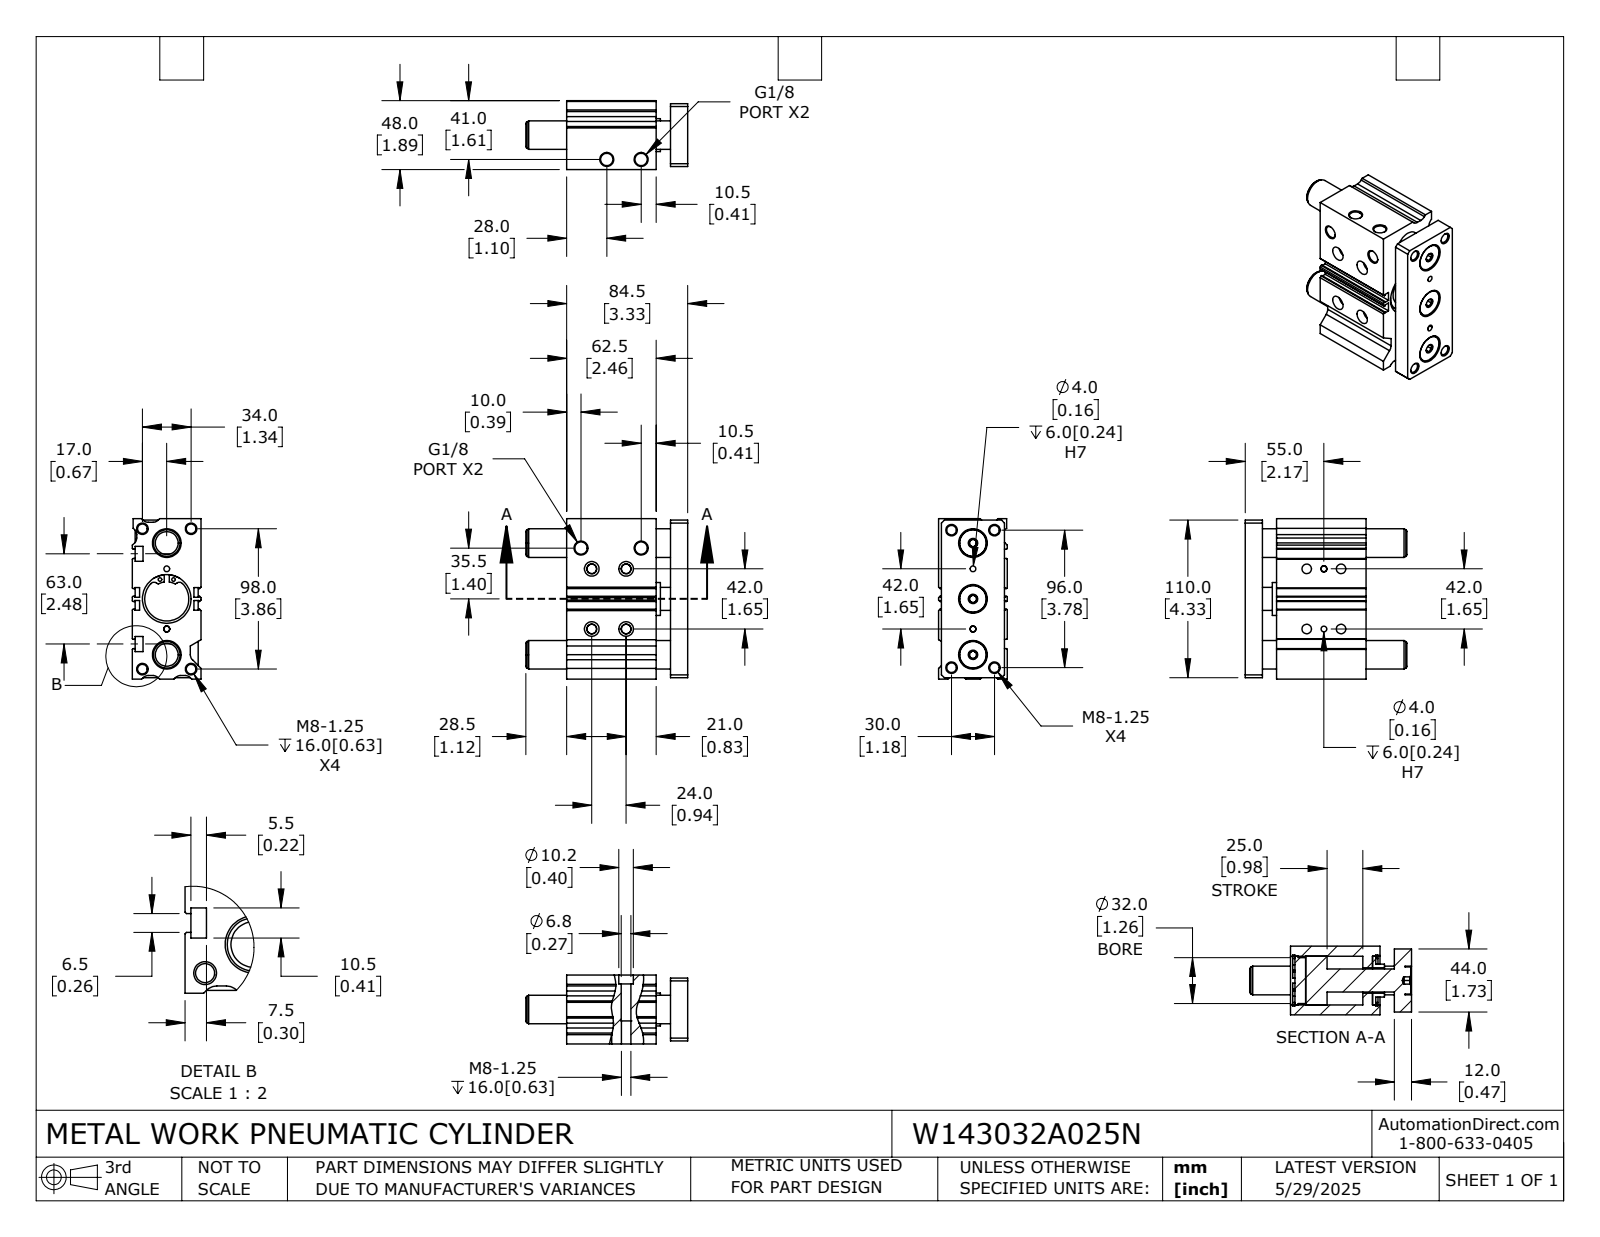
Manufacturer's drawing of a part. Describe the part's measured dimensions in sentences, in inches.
The part is named "W143032A025N_BODY; W143032A025N; W143032A025N_ROD". Its 3-D file was written by "SolidWorks 2024 (CONFIG_CONTROL_DESIGN)". It is 6 solids with 394 faces: 195 planar, 149 cylindrical and 50 other. Overall it measures 4.449 by 4.409 by 1.89 inches. Its volume is 21.55 cubic inches and its surface area 148.9 square inches. Round holes: 12 of diameter 0.262, 4 of diameter 0.098, 4 of diameter 0.157, 4 of diameter 0.268, 4 of diameter 0.337, 4 of diameter 0.402, 3 of diameter 0.197, 3 of diameter 0.787, 1 of diameter 0.697, 1 of diameter 1.211. Round bosses or shafts: 3 of diameter 0.748, 2 of diameter 1.406, 1 of diameter 1.339, 1 of diameter 1.26, 1 of diameter 0.906, 1 of diameter 0.63. Partial cylindrical surfaces (rounded edges, fillets, slot ends): 9 of radius 0.197, 4 of radius 0.079, 4 of radius 0.118, 2 of radius 0.507. The main face-to-face distances are 0.472, 0.118, 0.866, 1.89, 0.394, 2.461, 0.079, 0.295, 2.854, 3.327. The hole center spacings are 1.654, 0.088, 0.348, 0.472, 0.566, 0.689, 0.776, 1.019.
